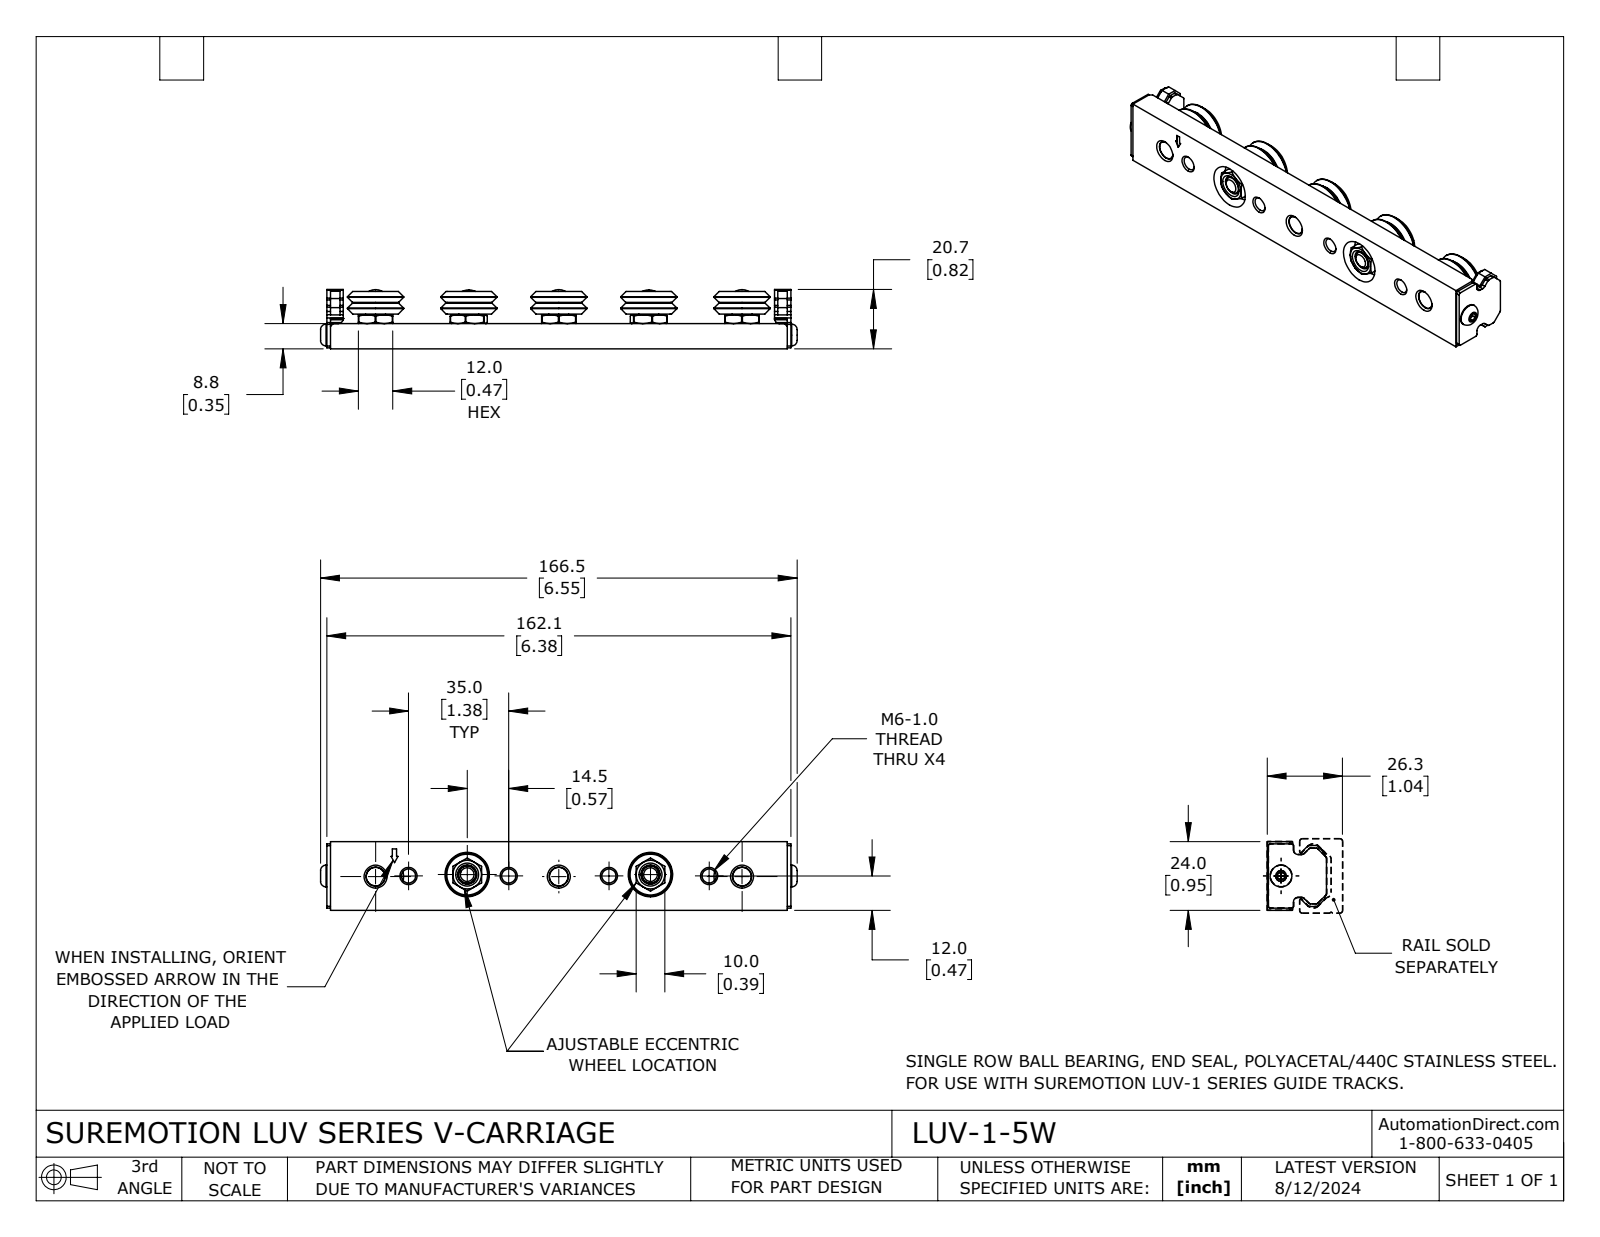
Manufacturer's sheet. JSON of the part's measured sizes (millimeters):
{"part_name": "LUV-1-5W", "step_written_by": "SolidWorks 2023 (CONFIG_CONTROL_DESIGN)", "units": "millimeters", "bodies": {"solids": 10, "faces": 942, "planar": 262, "cylindrical": 278, "other": 402}, "overall_size": [166.45, 24, 20.73], "volume_mm3": 46471, "surface_area_mm2": 24828, "round_holes": [[4.76, 5], [12.18, 5], [12.41, 5], [4.92, 4], [6.65, 4], [6.36, 2], [15.49, 2], [3.24, 1], [6.65, 1]], "round_bosses_or_shafts": [[19.58, 5], [8.46, 5], [8.23, 5], [4.75, 5], [8, 3], [5.99, 3], [14.25, 2], [6.3, 2]], "partial_cylinders_radius": [[0.38, 12], [0.84, 6], [6.84, 5], [0.64, 4], [1.6, 4], [1.78, 2]], "face_to_face_distances": [8.81, 24, 1.27, 160.79, 7.65, 11.23, 20.04, 6.14, 6.02, 13.9], "hole_center_spacings": [35, 0.61, 13.93, 14.51, 20.51, 21.07, 48.93, 49.5]}
